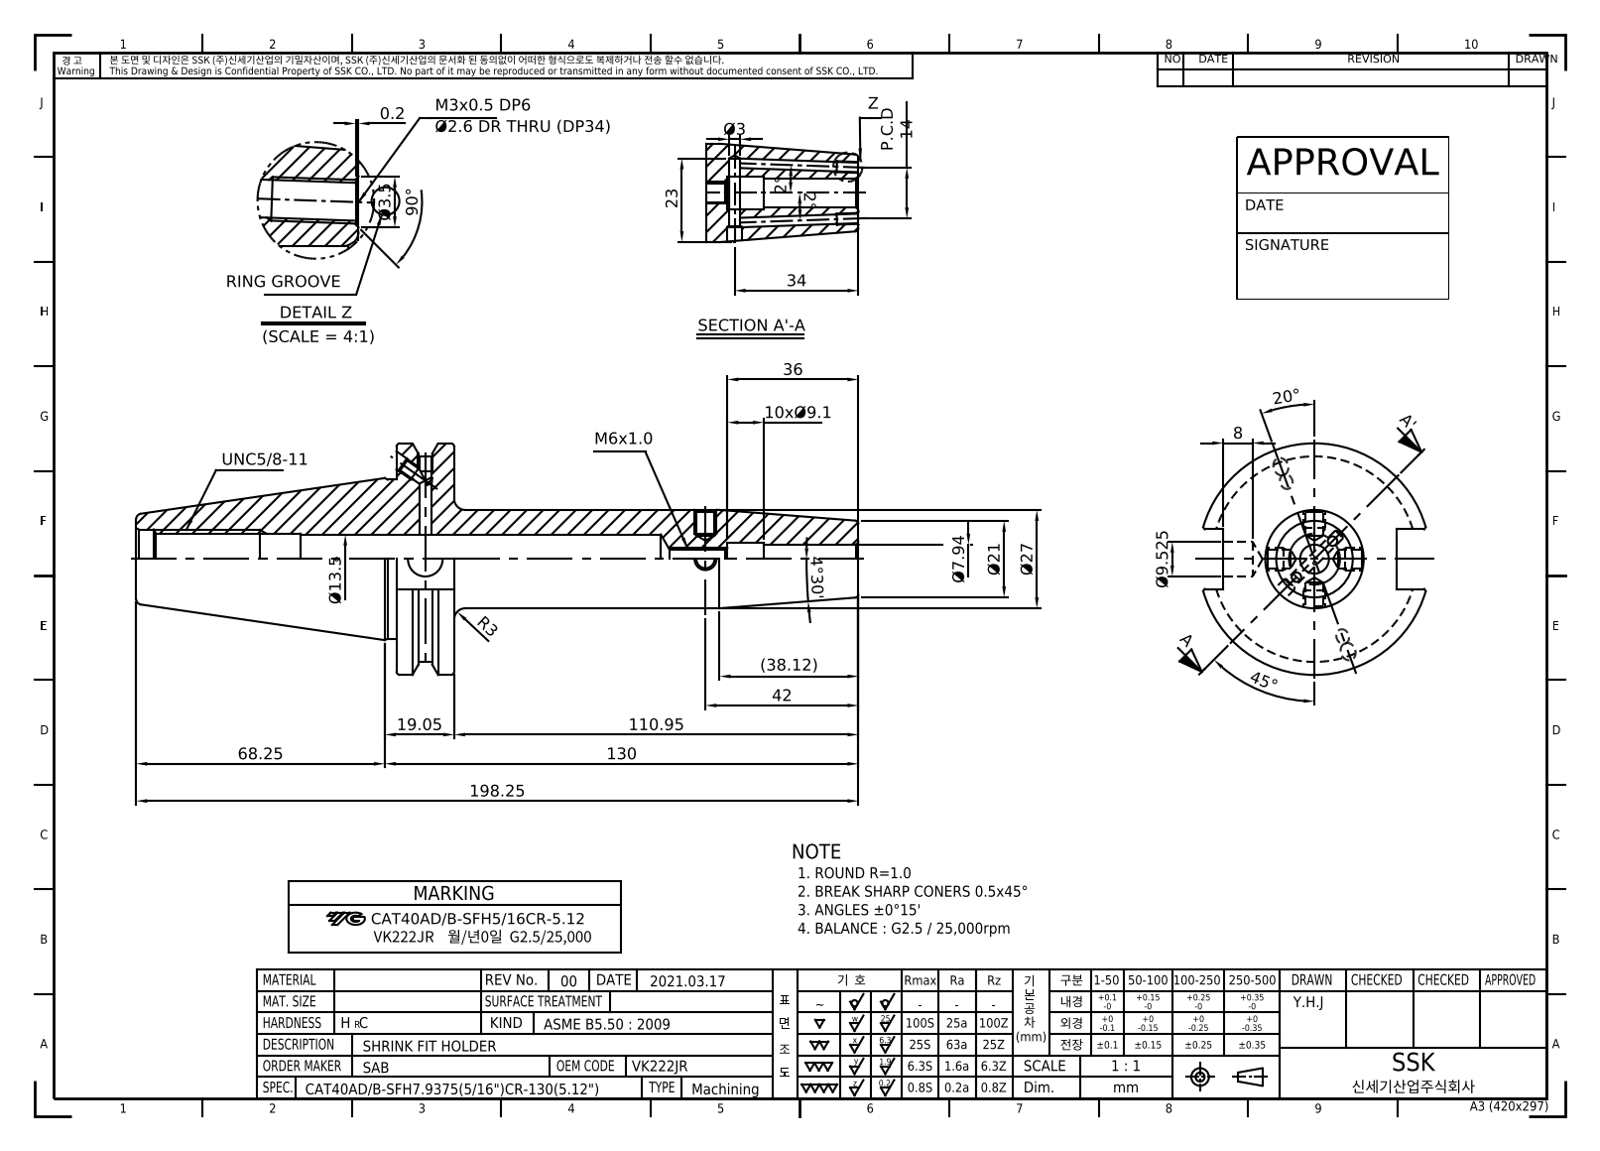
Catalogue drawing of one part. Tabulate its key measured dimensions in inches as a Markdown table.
| quantity | value |
| --- | --- |
| part name | LO-CAT40ADB-SFH7.9375CR-130 |
| STEP written by | Autodesk Inventor 2022 (AUTOMOTIVE_DESIGN) |
| units | inches |
| bodies | 1 solid, 91 faces (37 planar, 31 cylindrical, 23 other) |
| overall size | 7.805 × 2.5 × 2.405 |
| volume | 9.136 in³ |
| surface area | 52.15 in² |
| round holes (diameter × count) | 0.128 × 4, 0.097 × 2, 0.157 × 2, 0.165 × 2, 0.194 × 1, 0.313 × 1, 0.358 × 1, 0.375 × 1, 0.512 × 1, 0.527 × 1, 0.642 × 1 |
| round bosses / shafts (diameter × count) | 2.5 × 1, 1.717 × 1, 1.063 × 1 |
| partial cylindrical surfaces (radius × count) | 1.108 × 1 |
| main face-to-face distances | 0.625, 4.993, 4.368, 1.874, 0.645, 2.812, 3.437, 7.805, 3.05, 0.238 |
